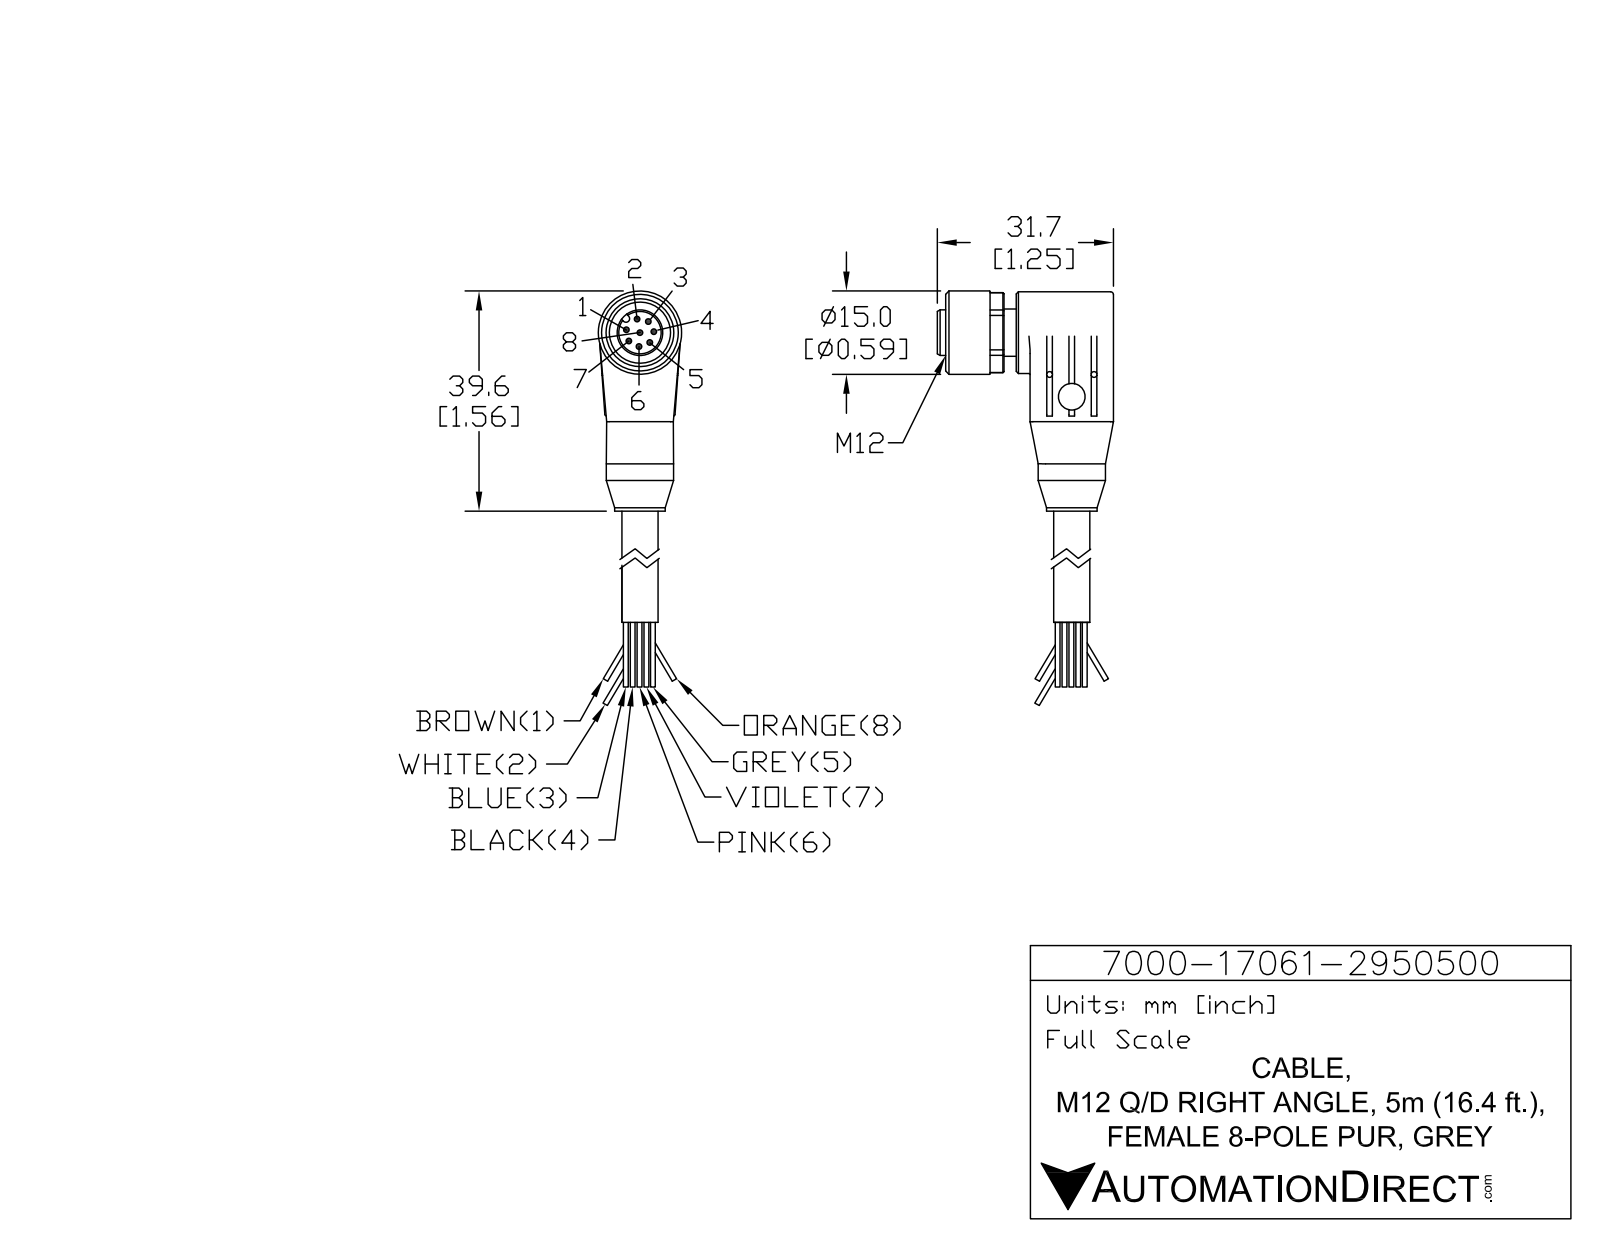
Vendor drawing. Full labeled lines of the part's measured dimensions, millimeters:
Part name (STEP PRODUCT): 7000-17061-2950500
STEP written by: SolidWorks 2015 (AUTOMOTIVE_DESIGN)
Units: millimetres
Bodies: 1 solid, 174 faces (73 planar, 67 cylindrical, 34 other)
Overall size (bounding box): 59.6 × 31.7 × 15
Volume: 9 094 mm³ · Surface area: 4 084 mm²
Round holes (diameter × count): ⌀1 ×8, ⌀1.05 ×4, ⌀4.8 ×1, ⌀11 ×1
Round bosses / shafts (diameter × count): ⌀15 ×1, ⌀14.7 ×1, ⌀12.1 ×1, ⌀9.1 ×1, ⌀8.5 ×1, ⌀8.2 ×1, ⌀6.5 ×1
Partial cylindrical surfaces — rounded edges, fillets, slot ends (radius × count): R0.5 ×4, R0.3 ×2, R0.65 ×1, R7.2 ×1
Main face-to-face distances: 2.5, 15, 4.7, 17.5, 19.7, 2.2, 3, 7.7, 12, 16.7
Hole centre spacings: 2.5, 2.07, 3.78, 4.95, 2.08, 4.22, 4.79, 4.8
